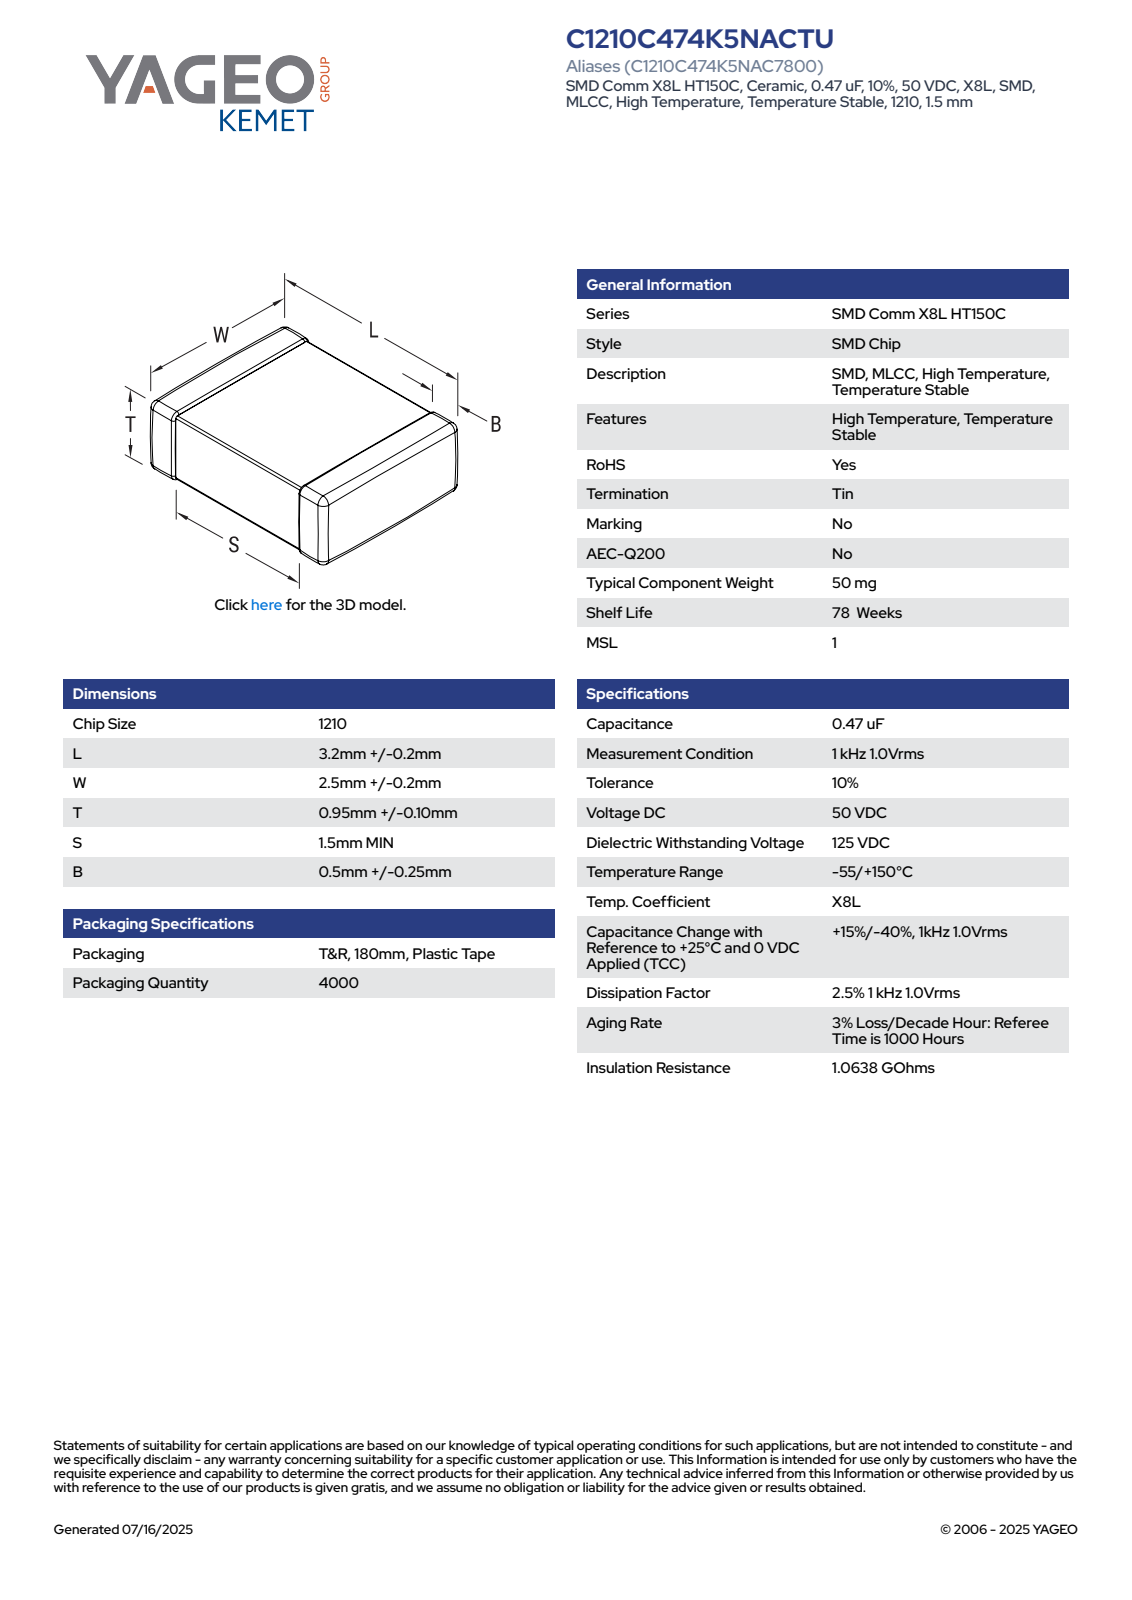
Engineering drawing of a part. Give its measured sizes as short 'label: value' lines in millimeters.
name: CCS_CCSTD_1210_L3.4W2.7S2.5T1.05B0.5
written by: SolidWorks 2021 (AUTOMOTIVE_DESIGN)
unit: mm
bodies: 4 solids, 125 faces (71 planar, 38 cylindrical, 16 other)
size: 3.4 × 2.7 × 1.05
volume: 9 mm³; area: 31 mm²
face distances: 0.99, 0.93, 1.05, 3.4, 2.64, 2.58, 2.7, 1, 0.94, 0.4
